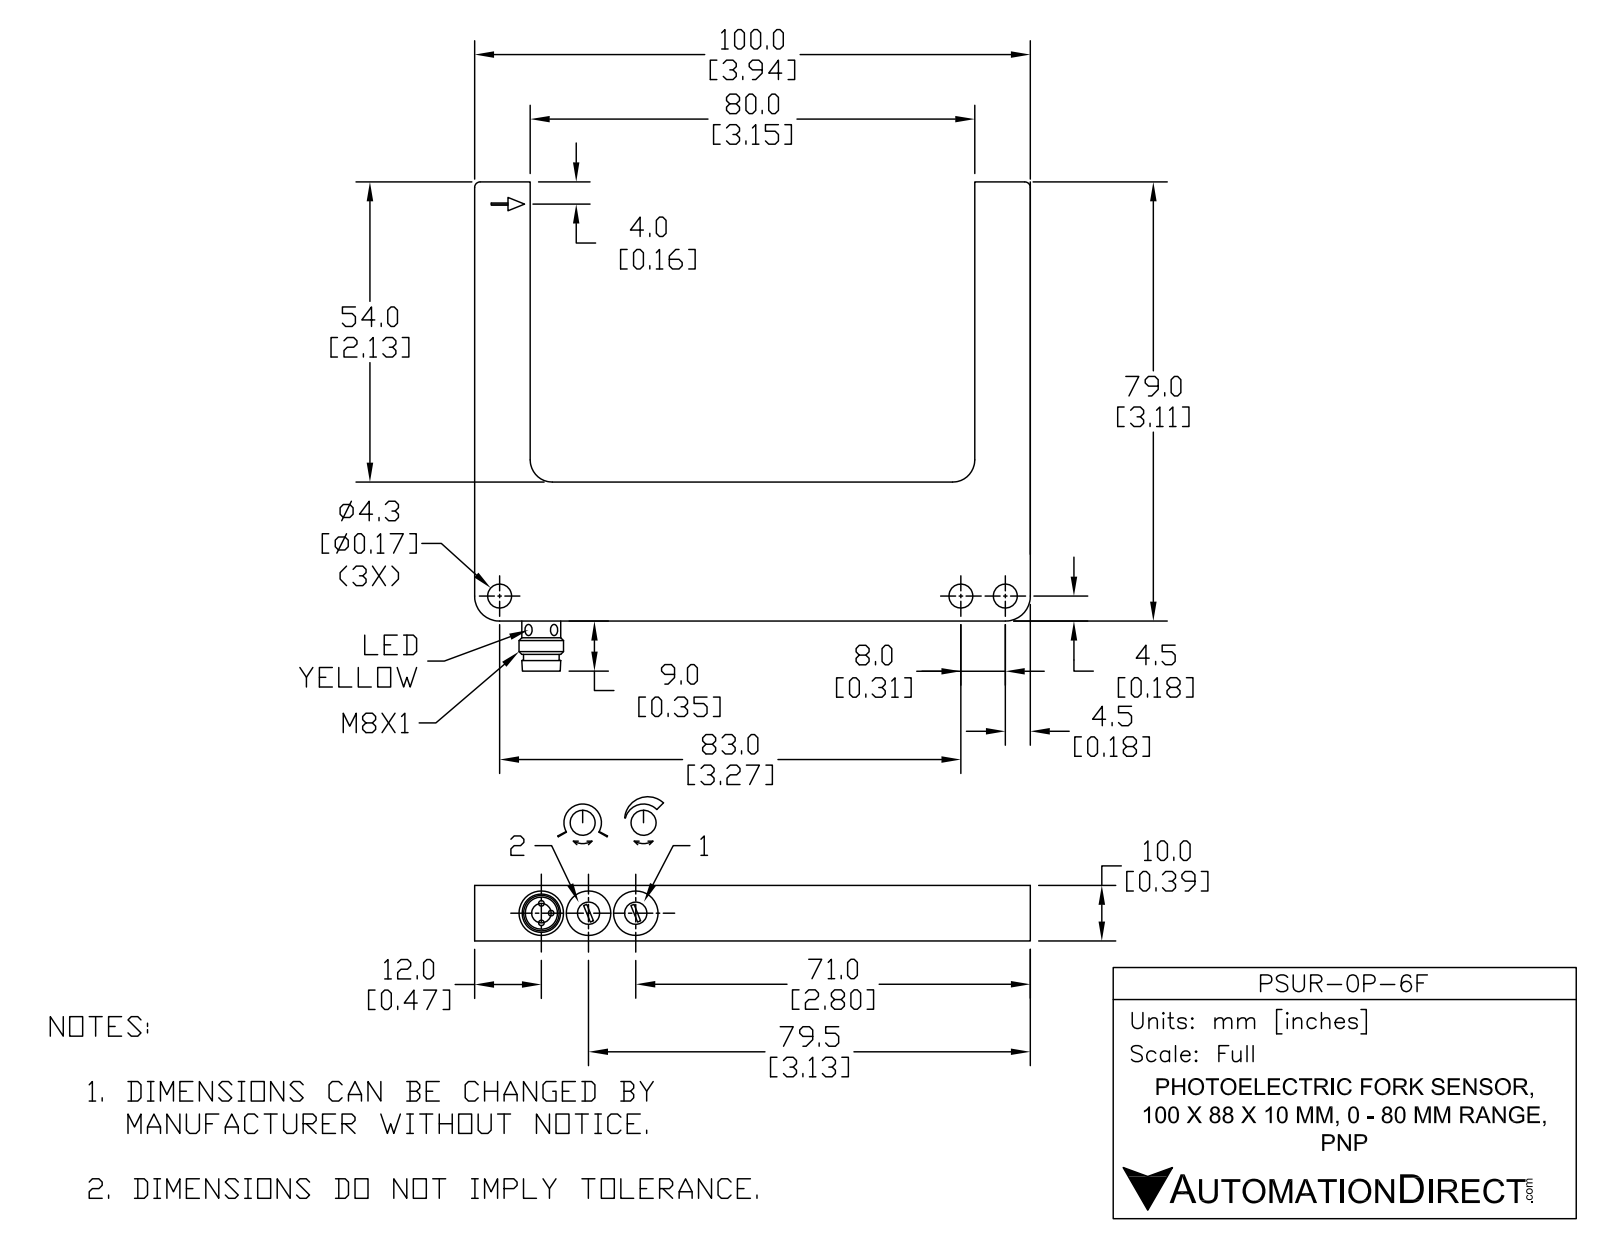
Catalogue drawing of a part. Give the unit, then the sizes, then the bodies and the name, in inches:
Units: inches
Overall size (bounding box): 3.937 × 3.465 × 0.394
Round holes (diameter × count): ⌀0.169 ×3, ⌀0.079 ×2, ⌀0.157 ×2, ⌀0.315 ×2, ⌀0.228 ×1
Round bosses / shafts (diameter × count): ⌀0.039 ×3, ⌀0.315 ×1, ⌀0.267 ×1
Partial cylindrical surfaces — rounded edges, fillets, slot ends (radius × count): R0.02 ×2, R0.039 ×2, R0.063 ×2, R0.157 ×2, R0.177 ×2
Main face-to-face distances: 0.394, 3.543, 3.937, 0.984, 3.15, 2.126, 3.11, 3.106, 0.98, 0.157
Hole centre spacings: 0.335, 0.315, 0.669, 3.268, 3.583
Volume: 2.17 in³ · Surface area: 19.25 in²
Bodies: 1 solid, 95 faces (35 planar, 48 cylindrical, 12 other)
Part name (STEP PRODUCT): PSUR-0P-6F
STEP written by: SolidWorks 2019 (AUTOMOTIVE_DESIGN)
